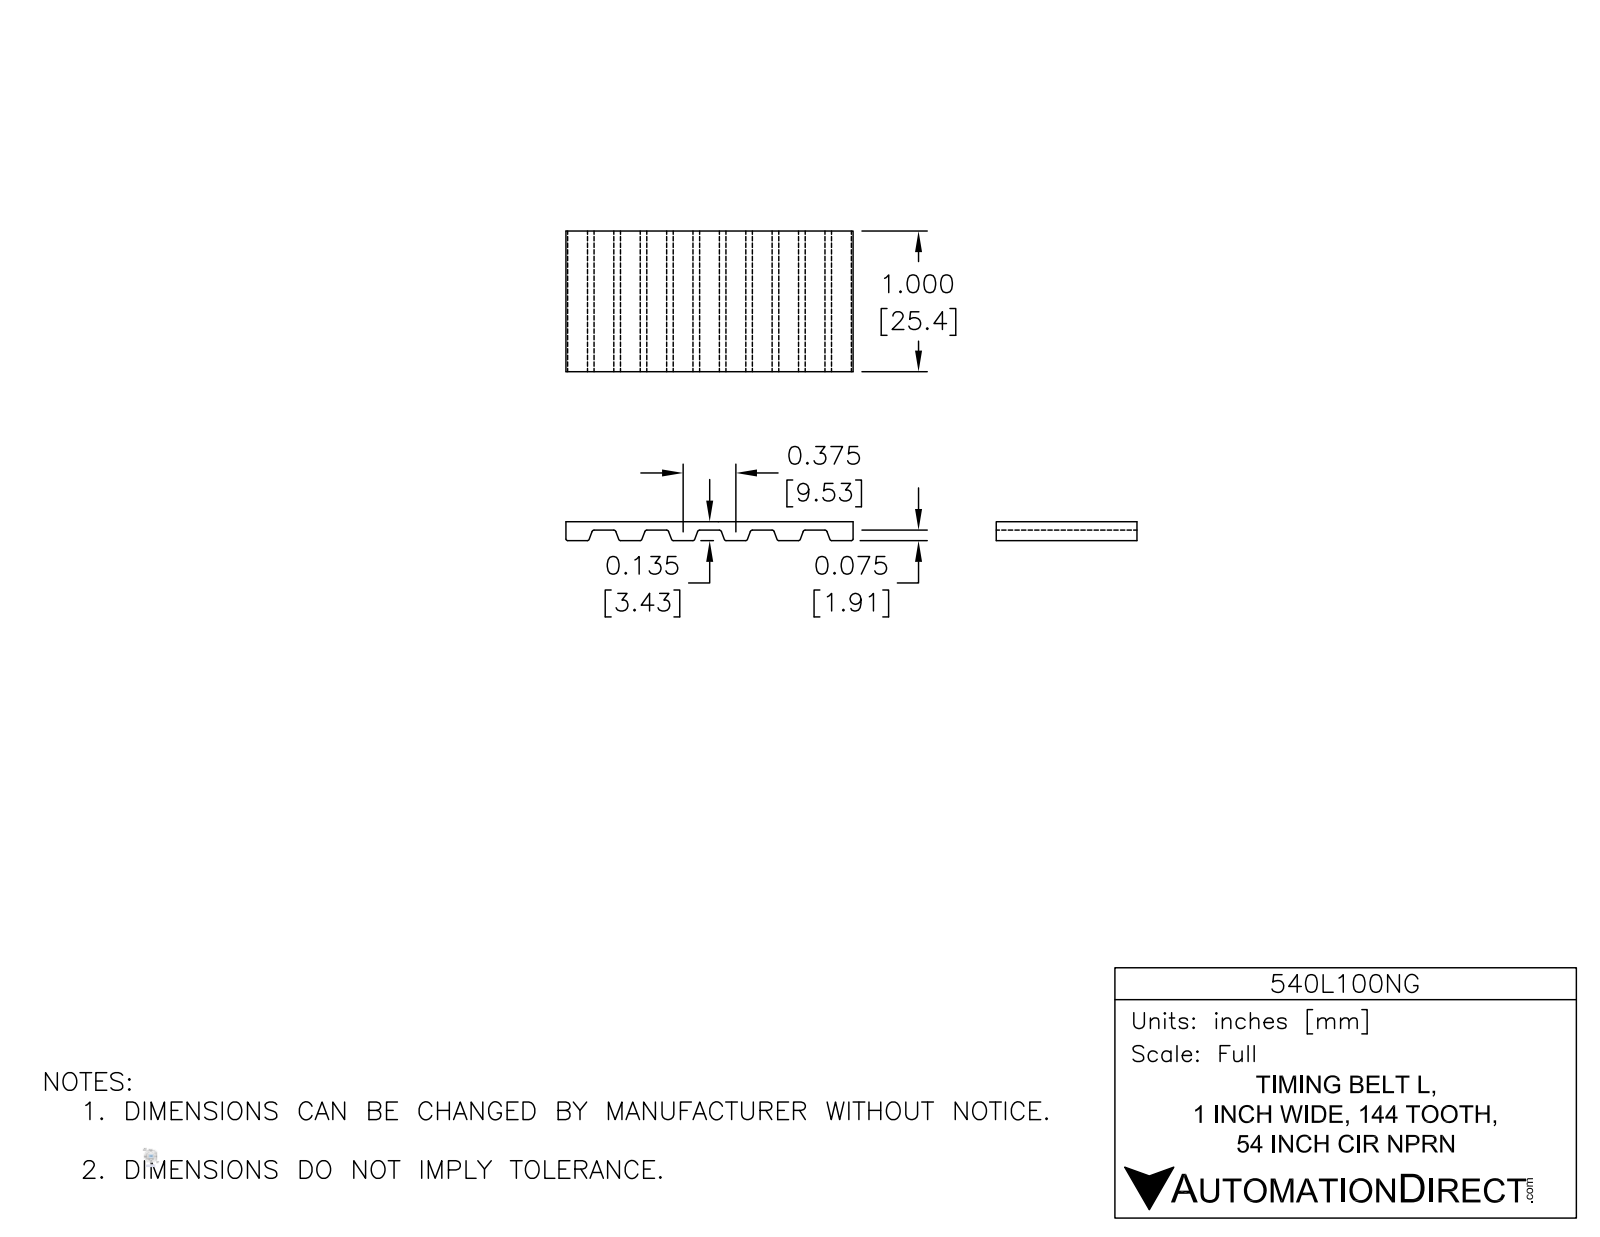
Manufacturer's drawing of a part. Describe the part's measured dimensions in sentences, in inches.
The part is named "540L100NG". Its 3-D file was written by "SolidWorks 2014 (AUTOMOTIVE_DESIGN)". It is 1 solid with 1168 faces: 553 planar, 615 cylindrical and 0 other. Overall it measures 25.288 by 3 by 1 inches. Its volume is 4.906 cubic inches and its surface area 130.4 square inches. Partial cylindrical surfaces (rounded edges, fillets, slot ends): 572 of radius 0.02, 2 of radius 1.435, 2 of radius 1.5. The main face-to-face distances are 0.065, 2.935, 3, 2.87, 0.14, 2.86, 0.075, 2.795, 1, 2.72.
